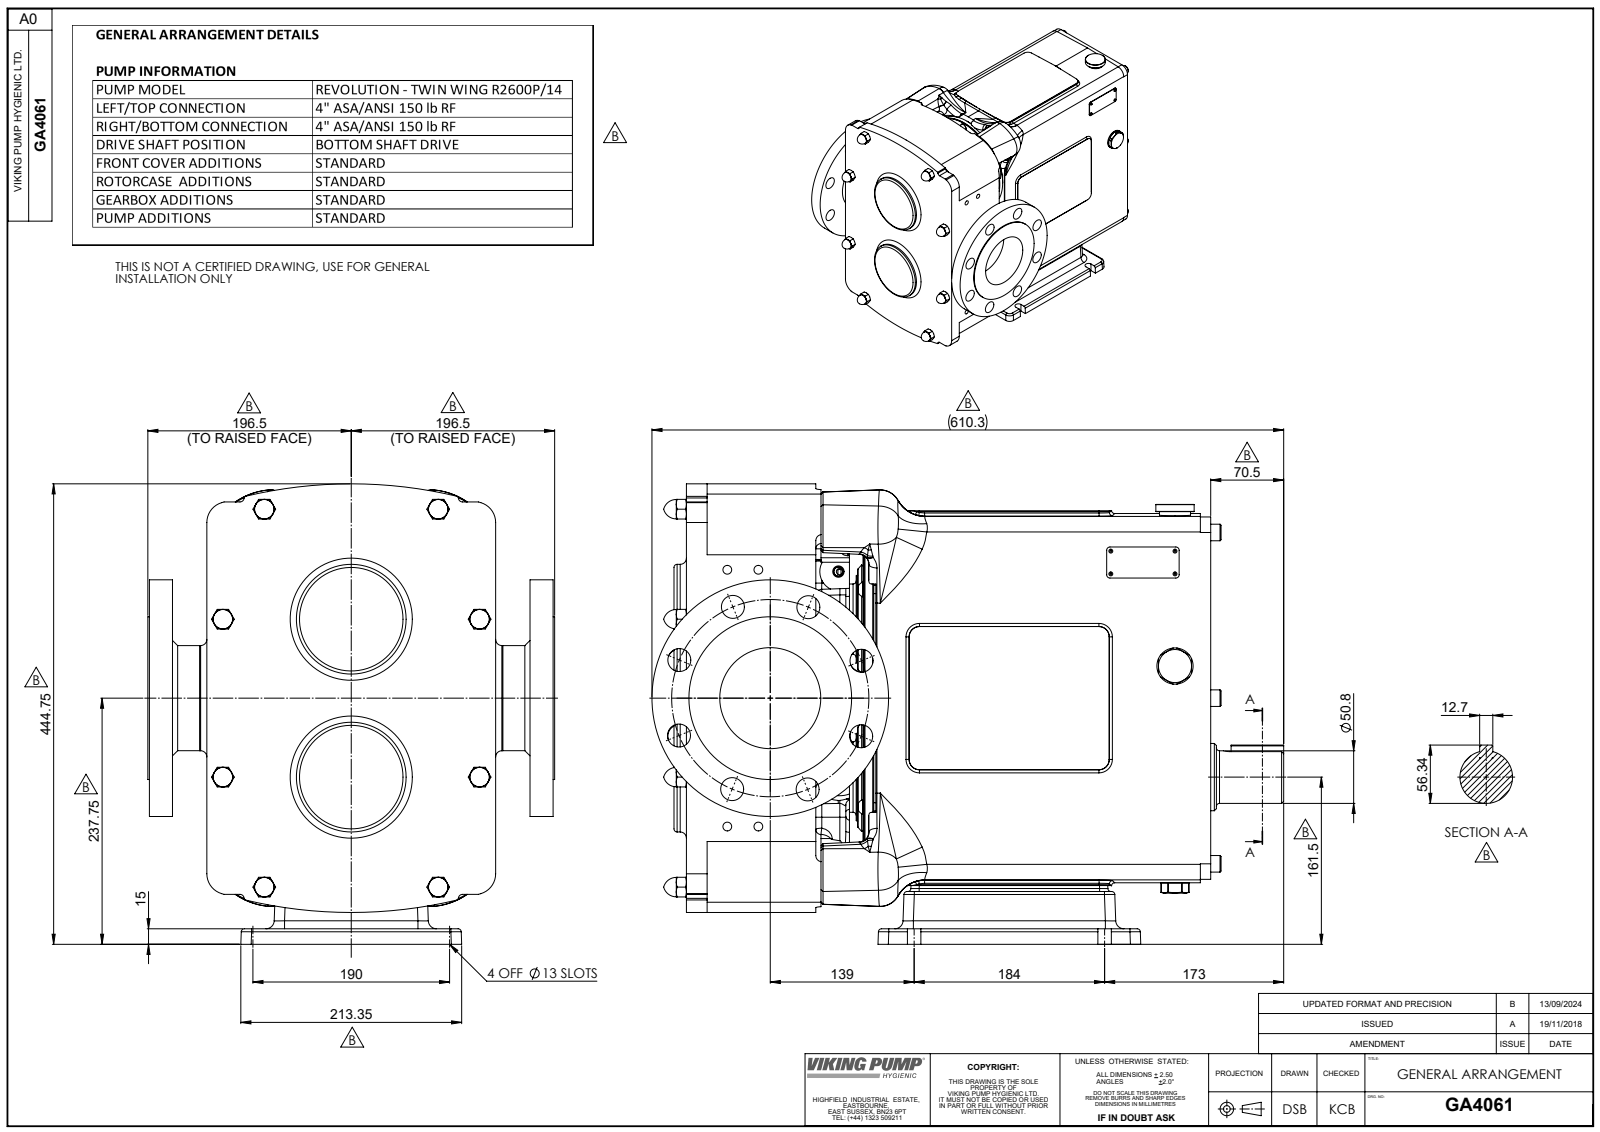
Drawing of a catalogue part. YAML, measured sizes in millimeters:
part_name: "Copy of Z94-5301-66 - 4 INCH ASA 150^GA4061; GA4061; Copy of R2600 CPP H BSD^GA4061"
step_written_by: "SolidWorks 2023 (AUTOMOTIVE_DESIGN)"
units: millimeters
bodies: {solids: 3, faces: 1592, planar: 449, cylindrical: 436, other: 707}
overall_size: [610.3, 444.75, 393]
volume: 42380000
surface_area: 1386000
round_holes:
  - {diameter: 22.2, count: 16}
  - {diameter: 6, count: 4}
  - {diameter: 8.5, count: 4}
  - {diameter: 149, count: 2}
  - {diameter: 35, count: 1}
  - {diameter: 97.6, count: 1}
round_bosses_or_shafts:
  - {diameter: 14, count: 10}
  - {diameter: 8, count: 10}
  - {diameter: 16, count: 6}
  - {diameter: 18, count: 4}
  - {diameter: 187, count: 2}
  - {diameter: 140, count: 2}
  - {diameter: 106, count: 2}
  - {diameter: 85, count: 2}
partial_cylinders:
  - {radius: 3, count: 44}
  - {radius: 6, count: 44}
  - {radius: 10, count: 28}
  - {radius: 0.2, count: 24}
  - {radius: 5, count: 16}
  - {radius: 8, count: 10}
  - {radius: 15, count: 8}
  - {radius: 20, count: 6}
face_to_face_distances: [193, 190, 506.5, 77.7, 267.7, 41.5, 74.7, 270.7, 3, 33.2]
hole_center_spacings: [72.9, 95.25, 134.7, 175.99, 190.49, 0.76, 72.2, 73.6]
